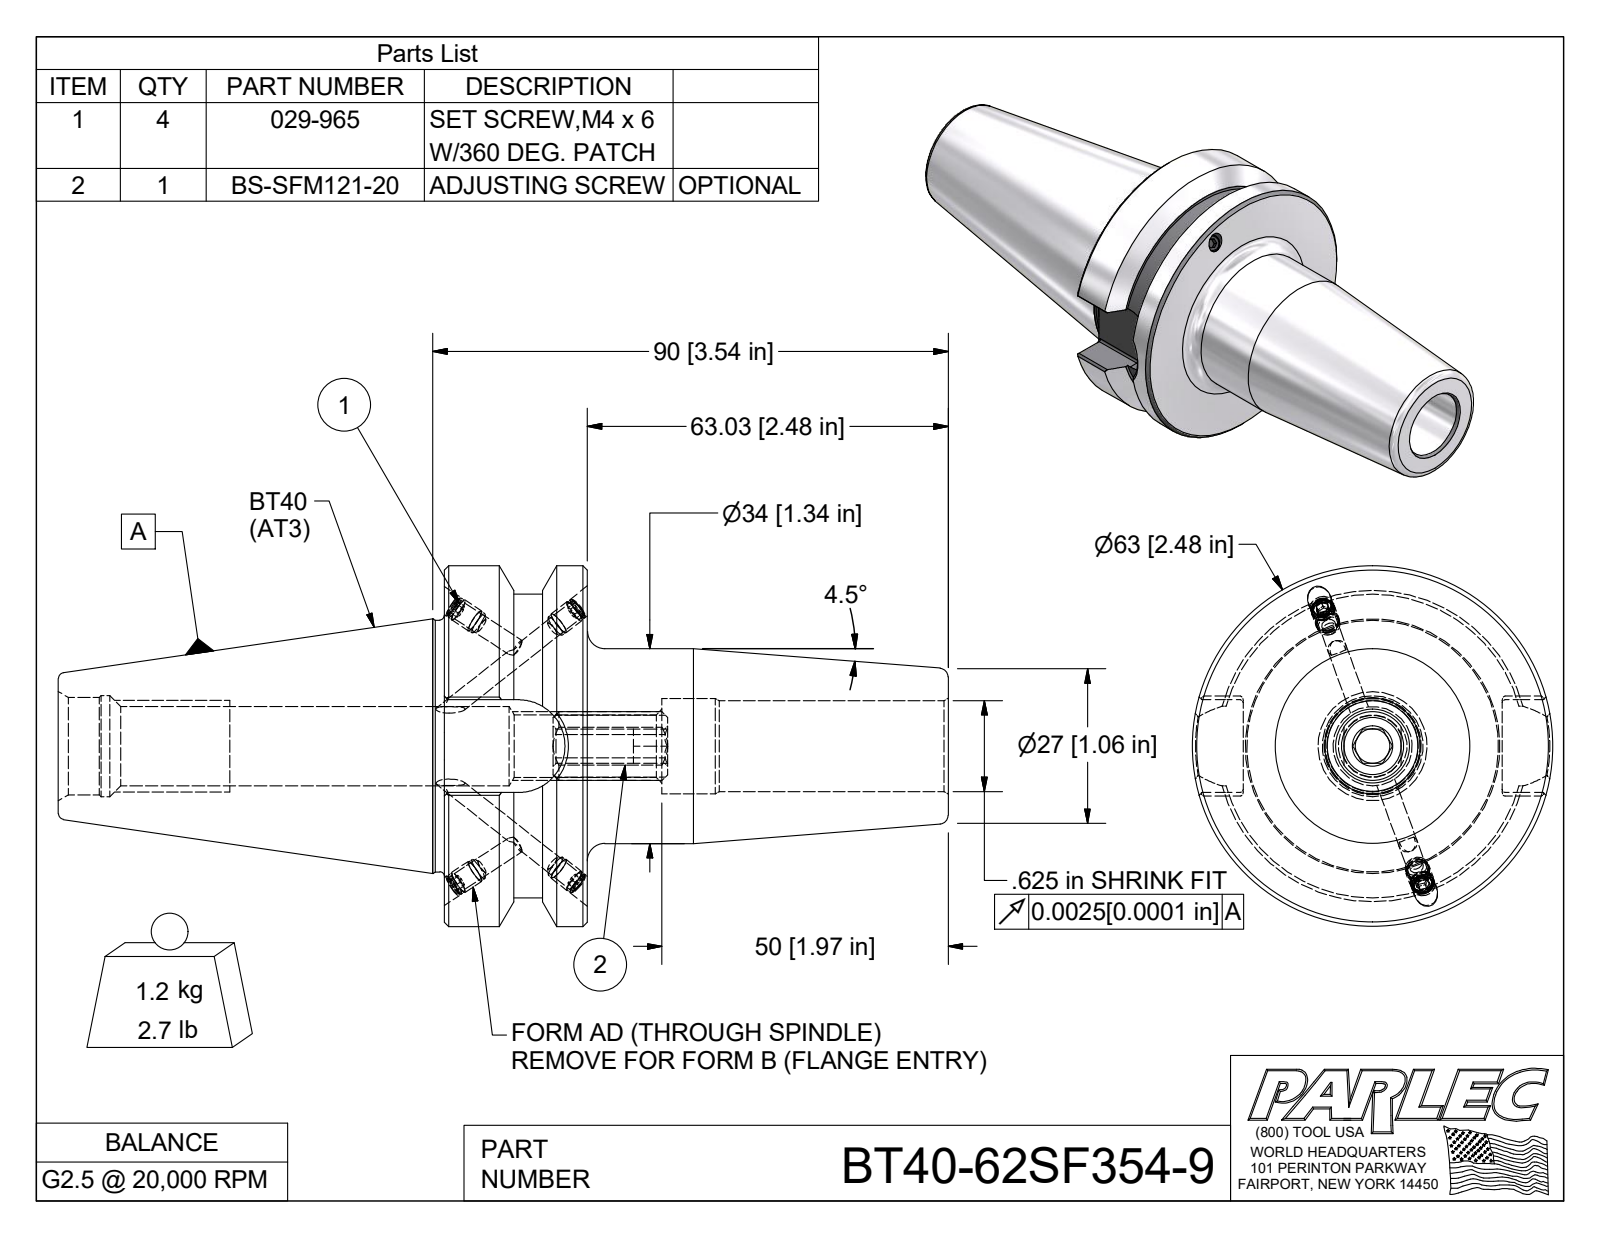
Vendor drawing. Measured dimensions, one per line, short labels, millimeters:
name: BT40-62SF354-9; BT40BC-62SF354-9-1; 029-965; BS-SFM121-20
written by: Autodesk Inventor 2009 (AUTOMOTIVE_DESIGN)
unit: mm
bodies: 6 solids, 173 faces (79 planar, 43 cylindrical, 51 other)
size: 155.4 × 63 × 63
volume: 159 400 mm³; area: 33 500 mm²
holes: 4× ⌀3.3, 4× ⌀4.1, 1× ⌀15.8, 1× ⌀16.6, 1× ⌀17.6
bosses: 4× ⌀4.2, 4× ⌀4, 1× ⌀63, 1× ⌀53, 1× ⌀44.5, 1× ⌀43.9, 1× ⌀34
rounds: 8× R0.5, 1× R6, 1× R8.1
face distances: 25, 45.2, 17.6, 27.6, 88, 63, 67.4, 92.4, 155.4, 16.2
